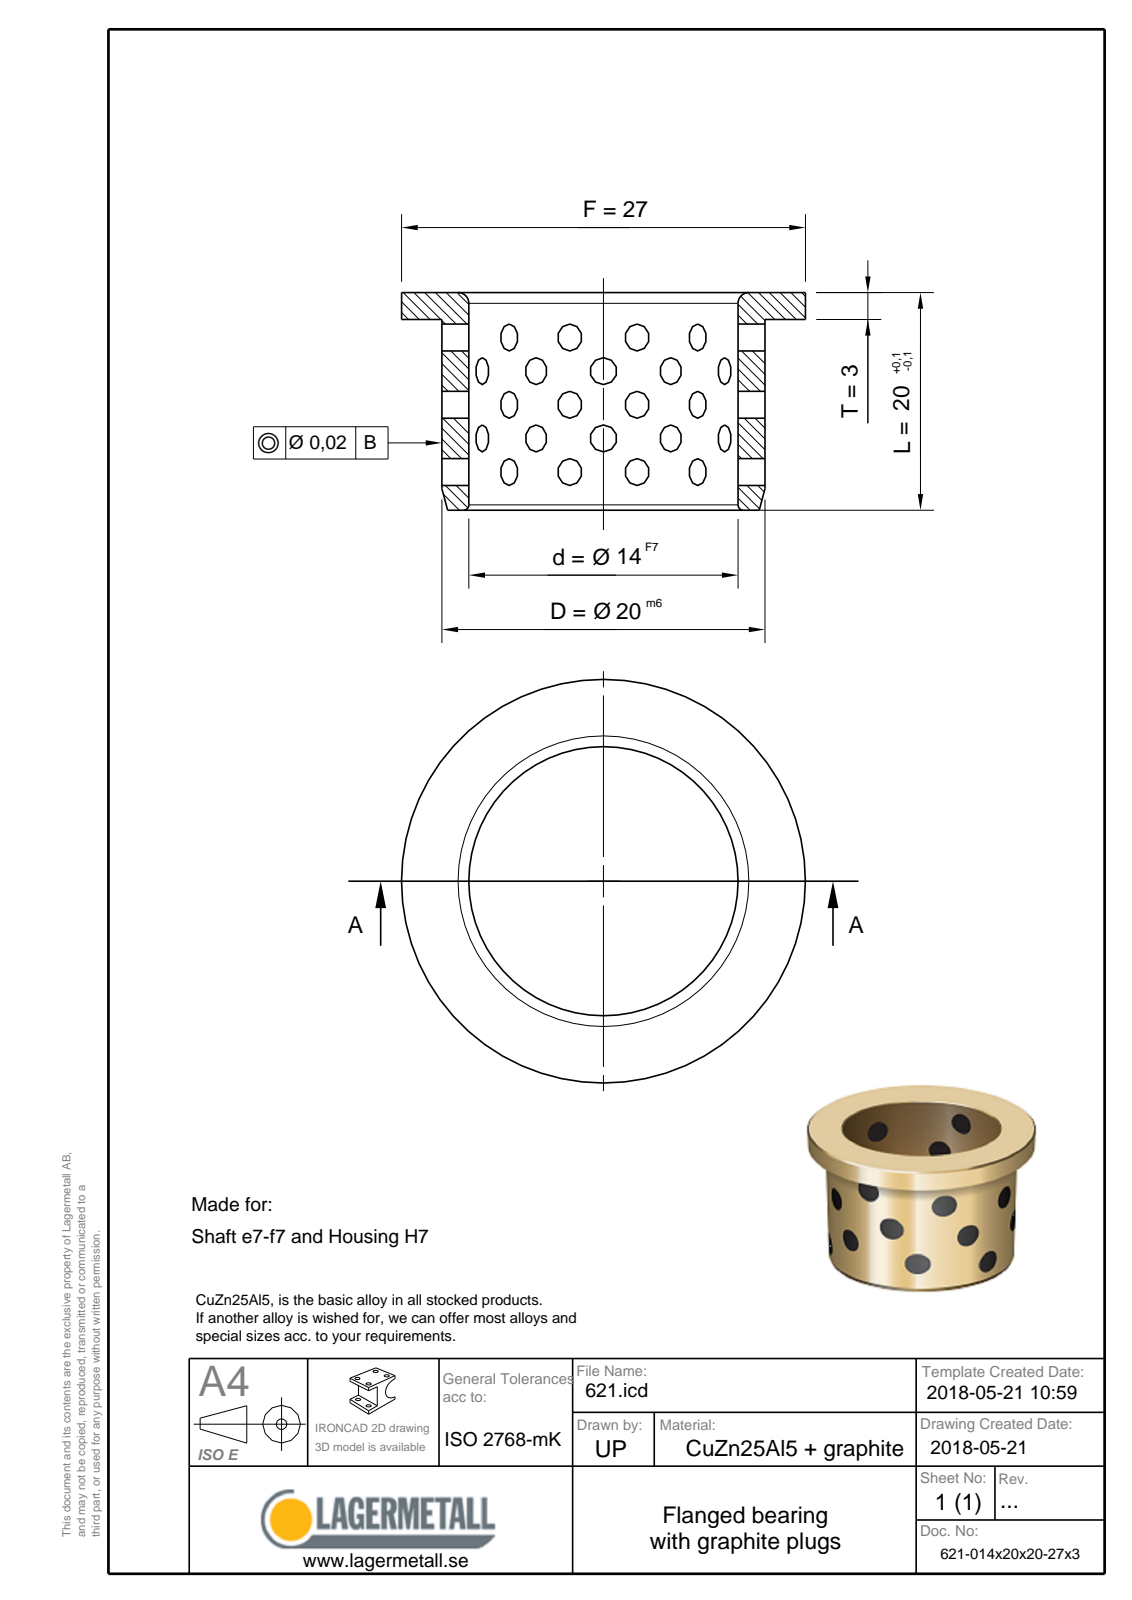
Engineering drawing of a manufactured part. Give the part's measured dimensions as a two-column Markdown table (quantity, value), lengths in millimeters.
| quantity | value |
| --- | --- |
| part name | 621-014x20x20-27x3 |
| STEP written by | Spatial InterOp 3D (CONFIG_CONTROL_DESIGN) |
| units | millimeters |
| bodies | 1 solid, 9 faces (3 planar, 3 cylindrical, 3 other) |
| overall size | 27 × 27 × 20 |
| volume | 3 891 mm³ |
| surface area | 2 943 mm² |
| round holes (diameter × count) | 14 × 1 |
| round bosses / shafts (diameter × count) | 27 × 1, 20 × 1 |
| main face-to-face distances | 3, 17, 20 |
